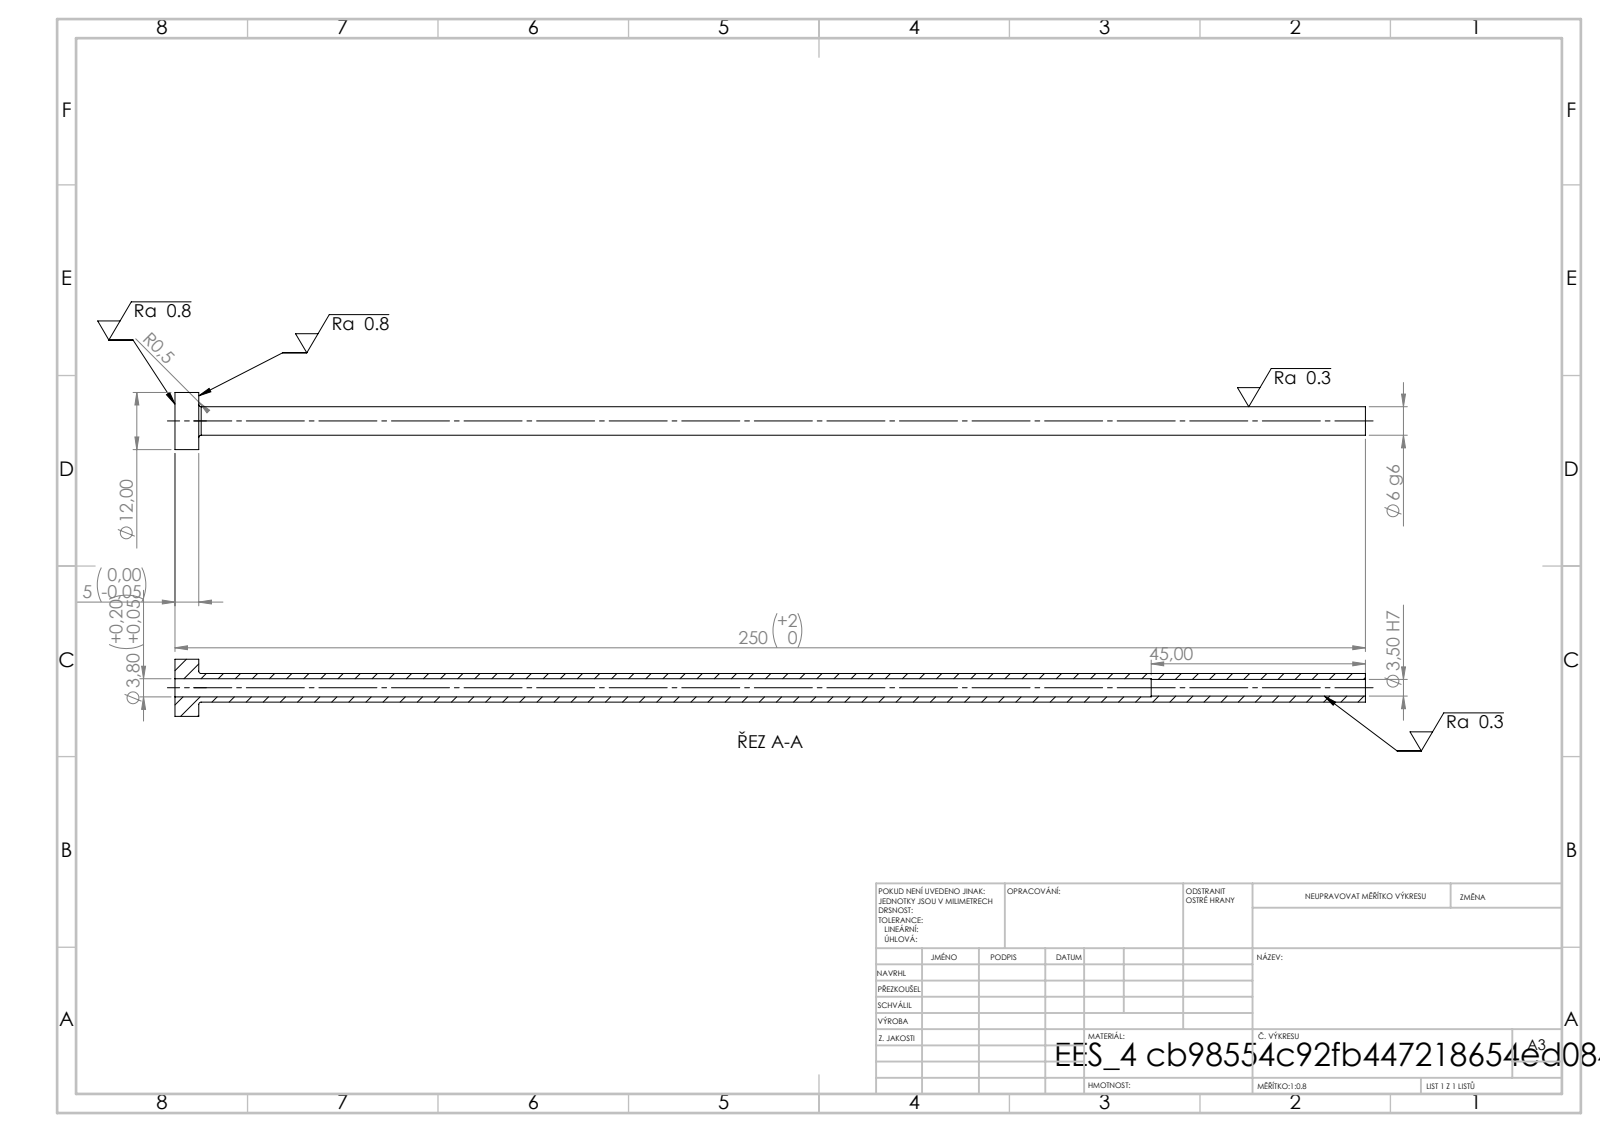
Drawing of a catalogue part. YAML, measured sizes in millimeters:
step_written_by: "SolidWorks 2019 (CONFIG_CONTROL_DESIGN)"
units: millimeters
bodies: {solids: 1, faces: 14, planar: 4, cylindrical: 8, other: 2}
overall_size: [250, 12, 12]
volume: 4736
surface_area: 7952
round_holes:
  - {diameter: 3.5, count: 1}
  - {diameter: 3.8, count: 1}
round_bosses_or_shafts:
  - {diameter: 12, count: 1}
  - {diameter: 6, count: 1}
face_to_face_distances: [5, 250, 245, 205, 200, 45]
